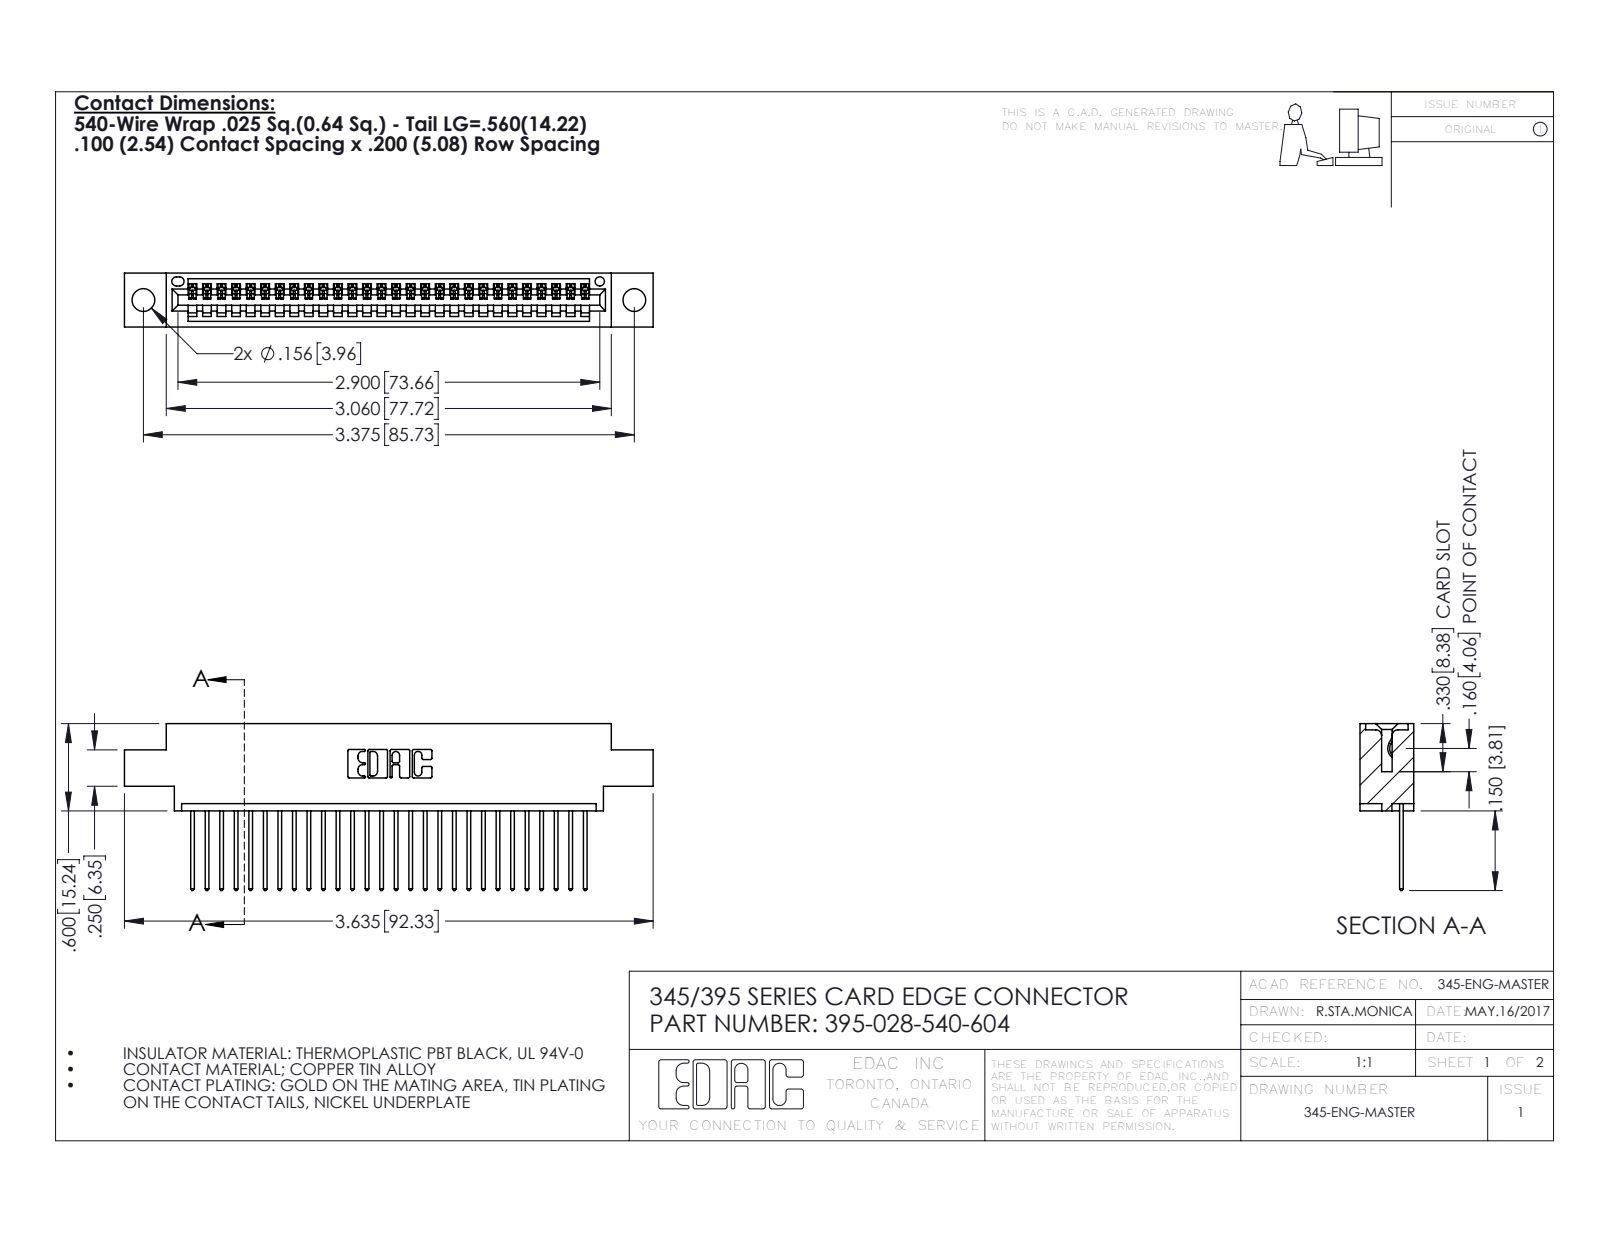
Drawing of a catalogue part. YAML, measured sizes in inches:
part_name: "345-292-001_345-293-140; 395-028-540-604; 345 Part_0.170 Offset - 0.156 Dia-TH"
step_written_by: "SolidWorks 2016 (CONFIG_CONTROL_DESIGN)"
units: inches
bodies: {solids: 29, faces: 1754, planar: 1204, cylindrical: 550, other: 0}
overall_size: [3.635, 1.147, 0.37]
volume: 0.518
surface_area: 17.52
round_holes:
  - {diameter: 0.156, count: 2}
  - {diameter: 0.064, count: 1}
partial_cylinders:
  - {radius: 0.006, count: 56}
  - {radius: 0.01, count: 56}
  - {radius: 0.01, count: 22}
  - {radius: 0.007, count: 6}
  - {radius: 0.031, count: 6}
  - {radius: 0.026, count: 3}
  - {radius: 0.031, count: 2}
  - {radius: 0.04, count: 2}
face_to_face_distances: [0.298, 0.072, 0.37, 0.2, 0.098, 0.272, 0.025, 0.225, 0.175, 0.149]
hole_center_spacings: [0.27, 3.14, 3.375]
